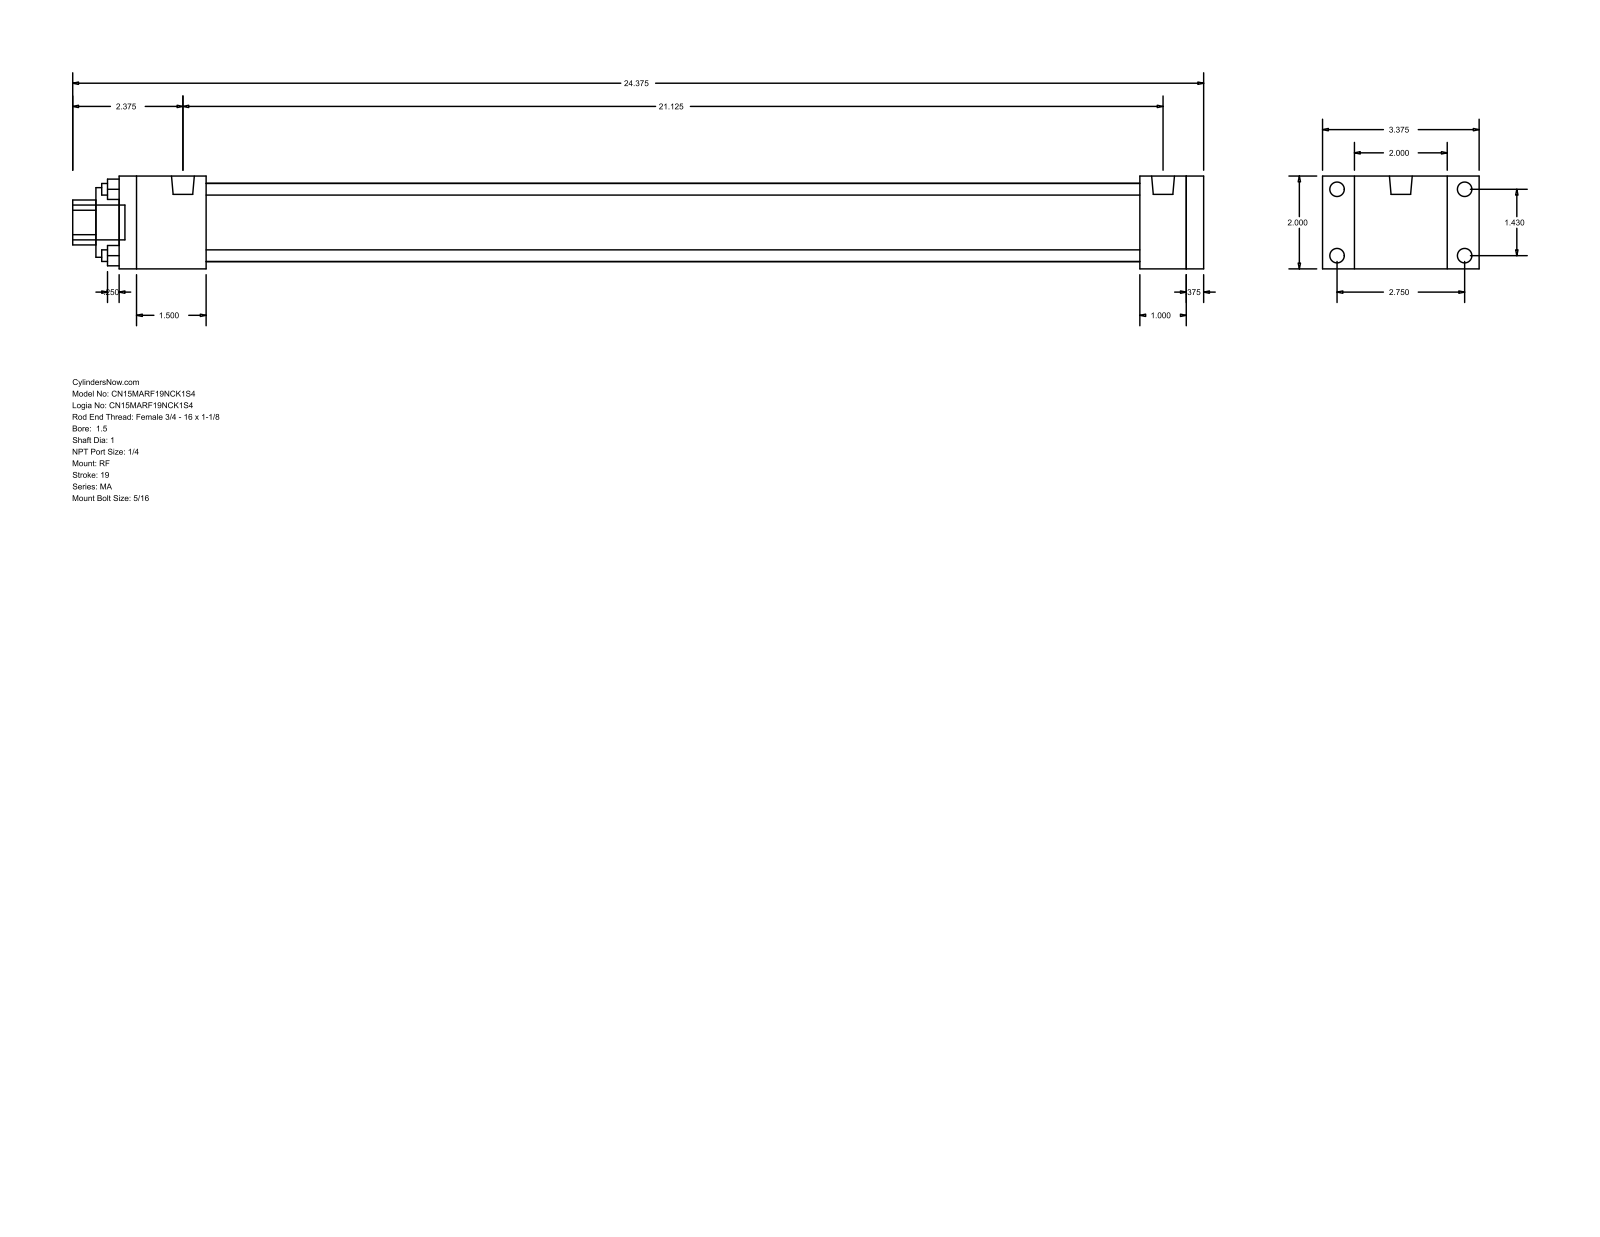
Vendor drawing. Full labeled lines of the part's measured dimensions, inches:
Part name (STEP PRODUCT): MA_RF__0150_1
STEP written by: GSSL Pune (CONFIG_CONTROL_DESIGN)
Units: inches
Bodies: 0 solids, 92 faces (64 planar, 28 cylindrical, 0 other)
Overall size (bounding box): 24.375 × 3.375 × 2
Round holes (diameter × count): ⌀0.25 ×4, ⌀1 ×1, ⌀1.5 ×1, ⌀1.69 ×1
Round bosses / shafts (diameter × count): ⌀0.313 ×8, ⌀0.492 ×2, ⌀0.75 ×1
Partial cylindrical surfaces — rounded edges, fillets, slot ends (radius × count): R0.484 ×1
Main face-to-face distances: 2, 0.375, 23.375, 23, 1, 22, 1.375, 1.875, 20.125, 21.125
Hole centre spacings: 1.011, 1.43, 2.022
